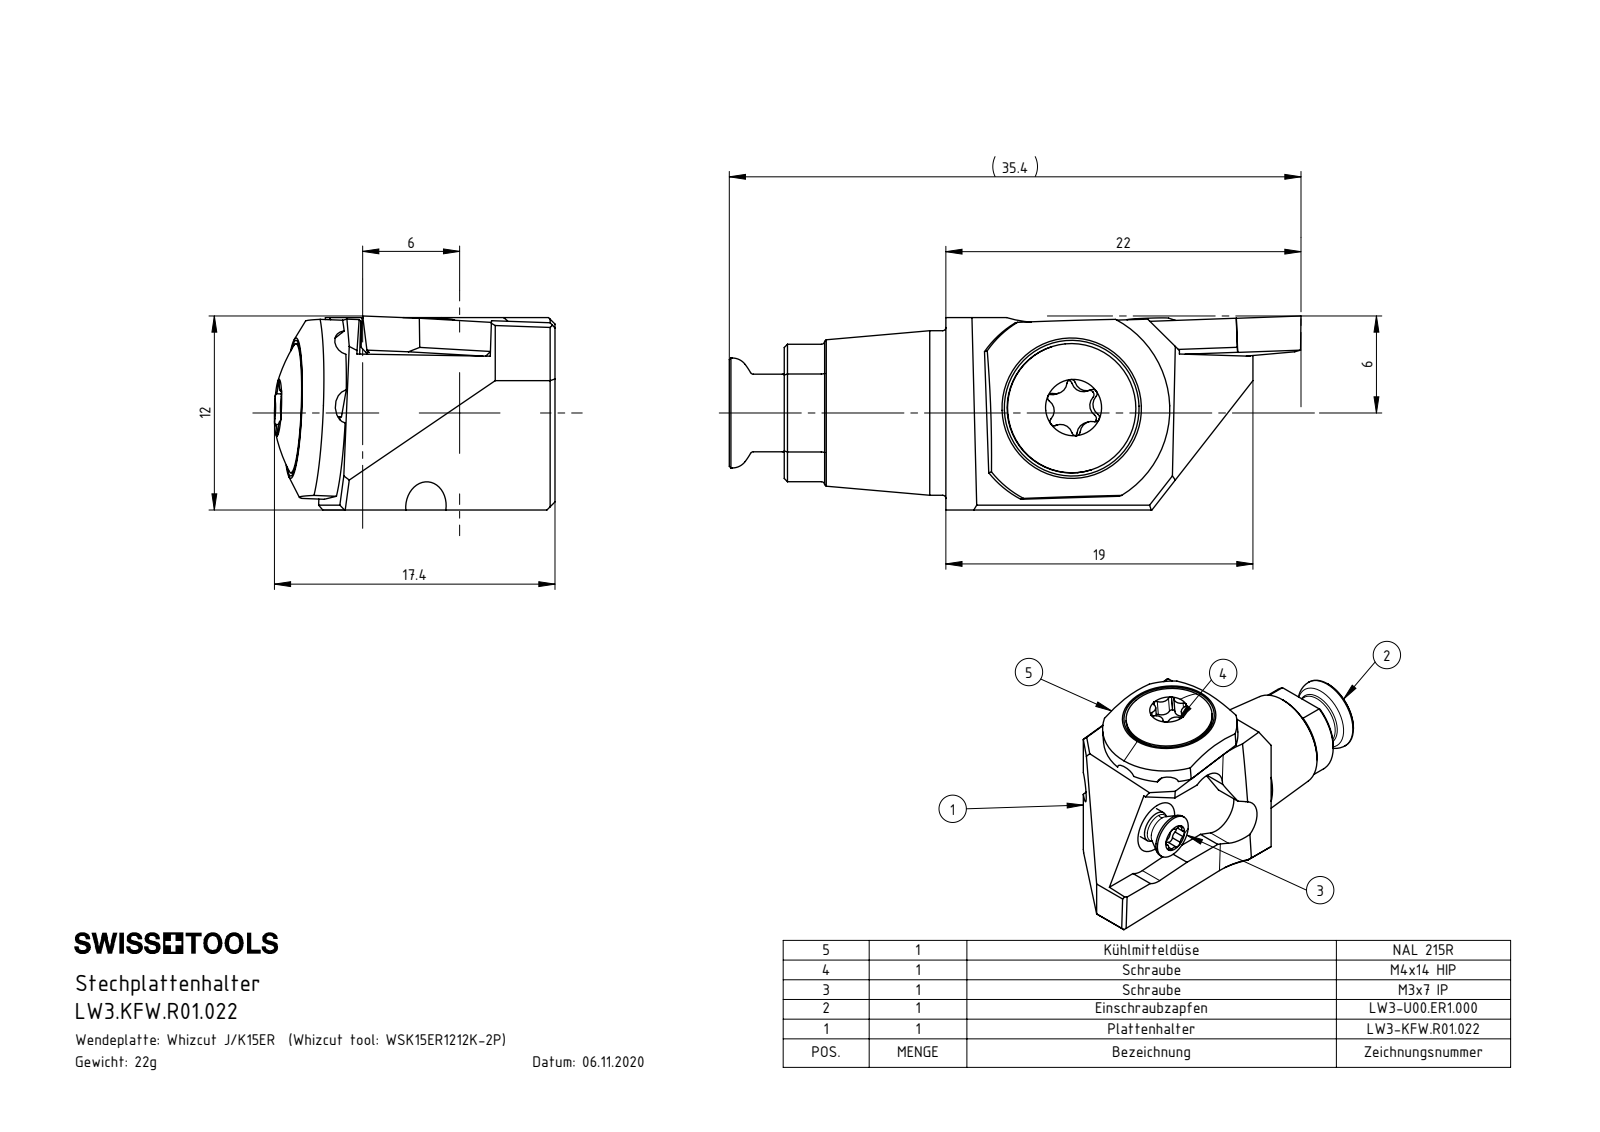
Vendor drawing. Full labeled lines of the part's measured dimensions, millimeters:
Part name (STEP PRODUCT): M4x14 HIP; M3x7 IP; LW3-U00.ER1.000_A; LW3-KFW.R01.022_A (+2 more)
STEP written by: SolidWorks 2017 (AUTOMOTIVE_DESIGN)
Units: millimetres
Bodies: 5 solids, 180 faces (69 planar, 51 cylindrical, 60 other)
Overall size (bounding box): 32.4 × 17.36 × 11.9
Volume: 3 134 mm³ · Surface area: 2 811 mm²
Round holes (diameter × count): ⌀2 ×2, ⌀2.5 ×2, ⌀3.3 ×1, ⌀5 ×1, ⌀5.5 ×1, ⌀6 ×1
Round bosses / shafts (diameter × count): ⌀4 ×2, ⌀10.18 ×1, ⌀8 ×1, ⌀6.8 ×1, ⌀6 ×1, ⌀5 ×1, ⌀4.8 ×1, ⌀4.2 ×1
Partial cylindrical surfaces — rounded edges, fillets, slot ends (radius × count): R0.4 ×6, R0.45 ×6, R2.25 ×3, R0.2 ×2, R4.25 ×2, R1.75 ×1, R6.25 ×1, R7 ×1
Main face-to-face distances: 2.2, 11.9, 2, 13.4, 11.4, 3.4, 8, 10, 7, 2.21
